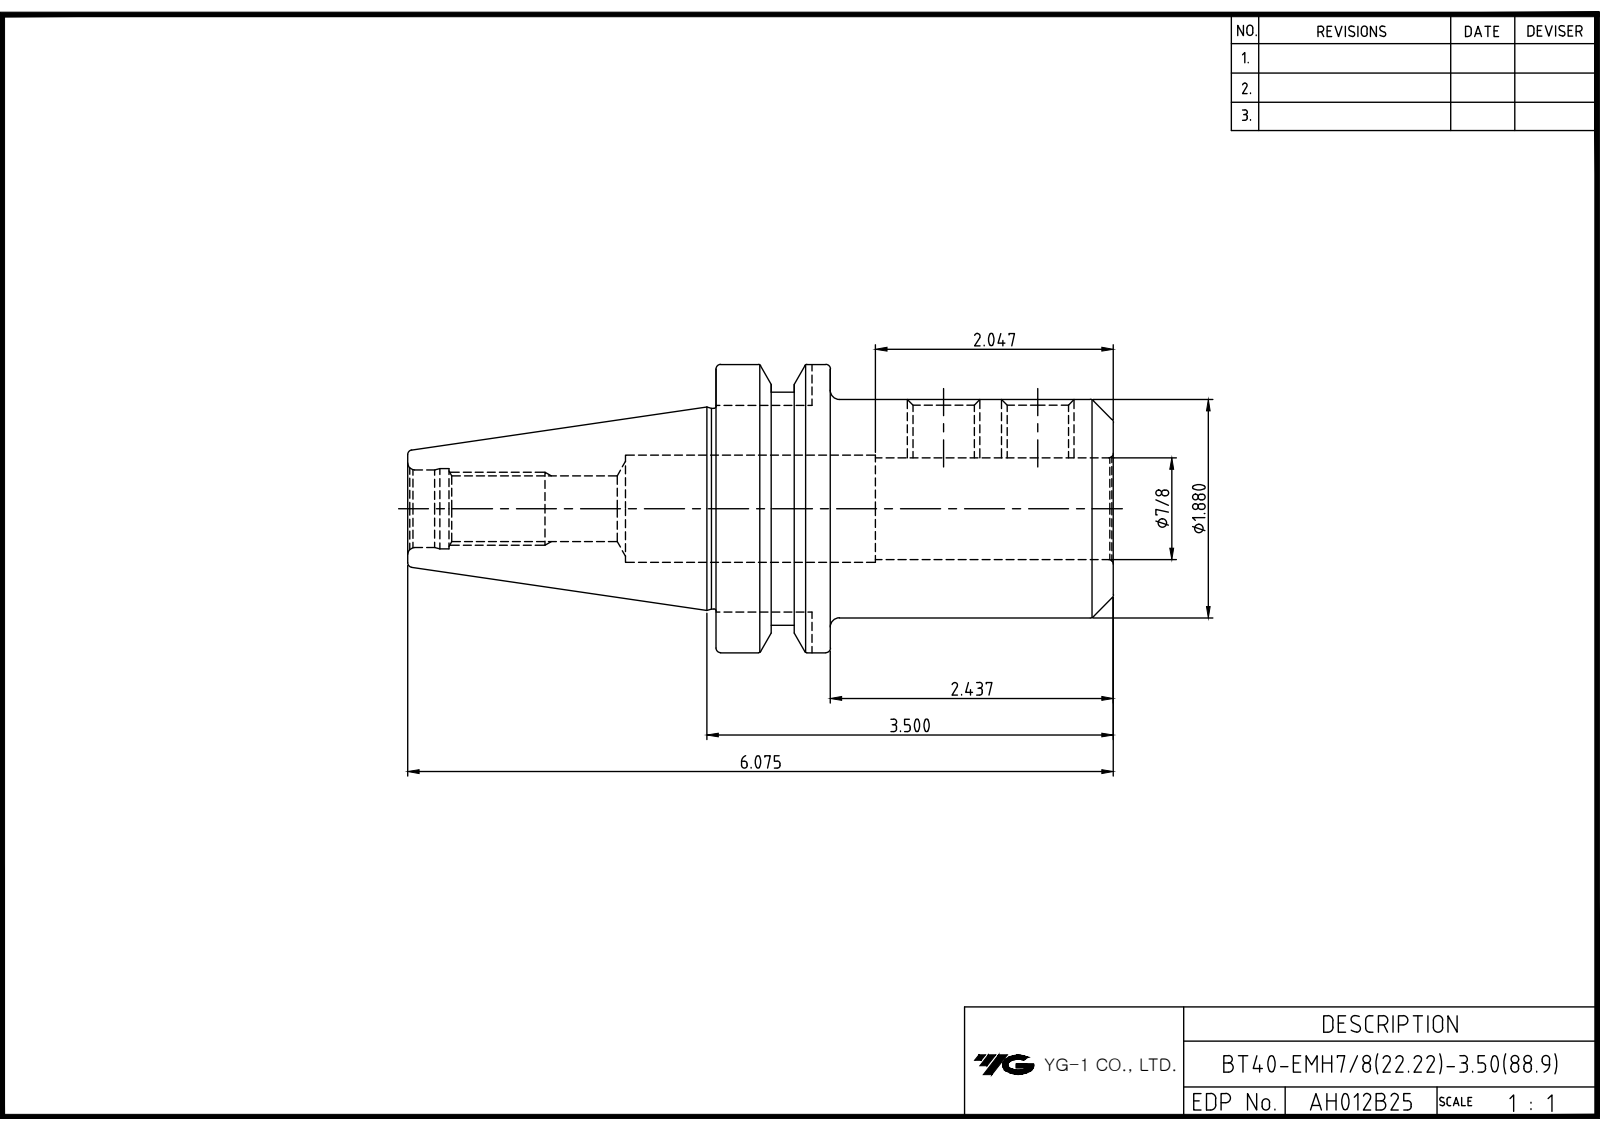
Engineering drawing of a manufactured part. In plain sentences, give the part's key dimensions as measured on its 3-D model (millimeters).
The part is named "LO-BT40-EMH22.225-88.9". Its 3-D file was written by "Autodesk Inventor 2022 (AUTOMOTIVE_DESIGN)". It is 1 solid with 55 faces: 18 planar, 16 cylindrical and 21 other. Overall it measures 154.3 by 63 by 63 millimeters. Its volume is 187 422 cubic millimeters and its surface area 37 364 square millimeters. Round holes: 2 of diameter 14.35, 1 of diameter 13.84, 1 of diameter 17, 1 of diameter 17.6, 1 of diameter 22.23, 1 of diameter 23.43. Round bosses or shafts: 1 of diameter 63, 1 of diameter 52.6, 1 of diameter 47.75, 1 of diameter 44. Partial cylindrical surfaces (rounded edges, fillets, slot ends): 1 of radius 8.05. The main face-to-face distances are 25, 86.9, 61.9, 45.2, 16.1, 67.4, 92.4, 154.3, 84.5, 17.1. The hole center spacings are 20.6.
